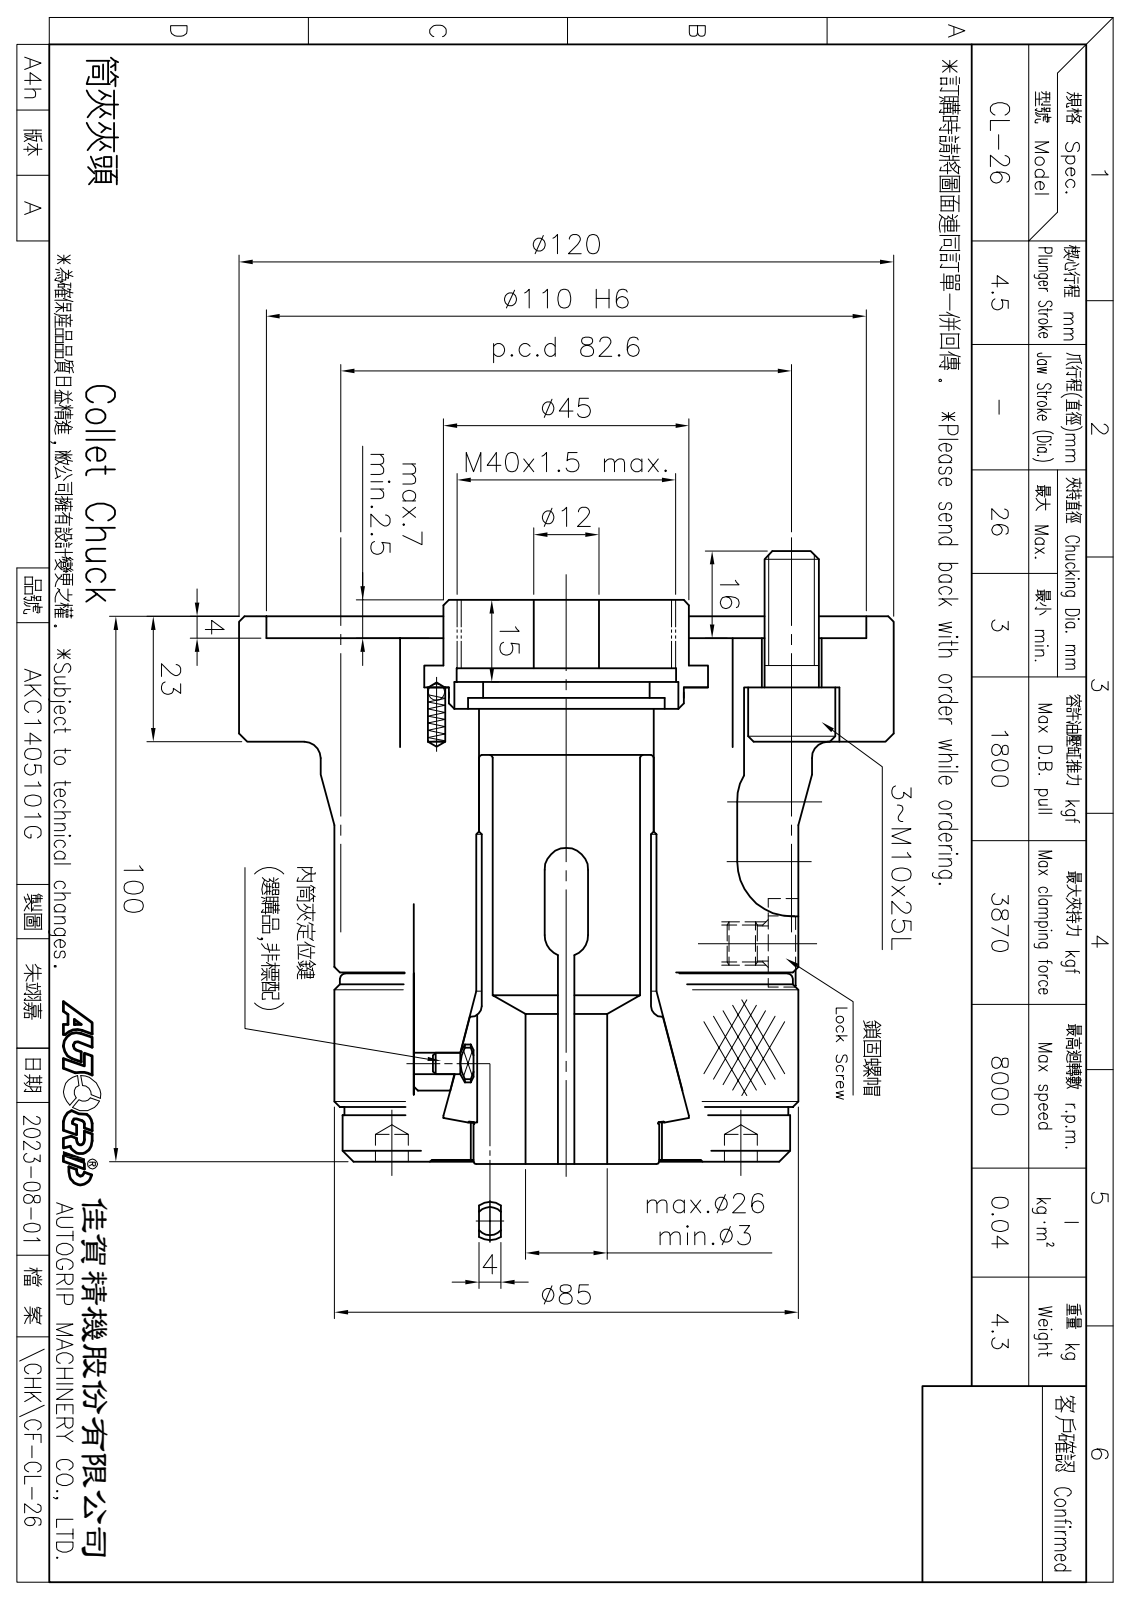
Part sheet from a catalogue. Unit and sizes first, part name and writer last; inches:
Units: inches
Overall size (bounding box): 4.724 × 4.724 × 4.409
Round holes (diameter × count): ⌀0.197 ×3, ⌀0.433 ×3, ⌀0.689 ×3, ⌀0.268 ×1, ⌀1.063 ×1, ⌀1.26 ×1, ⌀1.299 ×1, ⌀1.378 ×1, ⌀1.417 ×1, ⌀1.516 ×1, ⌀1.583 ×1, ⌀1.693 ×1
Round bosses / shafts (diameter × count): ⌀0.63 ×3, ⌀0.394 ×3, ⌀4.724 ×1, ⌀3.543 ×1, ⌀3.346 ×1, ⌀3.268 ×1, ⌀3.228 ×1, ⌀3.205 ×1
Partial cylindrical surfaces — rounded edges, fillets, slot ends (radius × count): R0.335 ×3, R0.394 ×3, R0.148 ×2, R0.315 ×1, R0.325 ×1
Main face-to-face distances: 0.354, 0.335, 3.425, 0.748, 3.031, 2.697, 0.512, 3.78, 3.445, 0.394
Hole centre spacings: 1.626, 2.817, 0.83, 1.24, 2.045, 2.77, 2.48
Volume: 33.63 in³ · Surface area: 207.7 in²
Bodies: 9 solids, 316 faces (97 planar, 114 cylindrical, 105 other)
Part name (STEP PRODUCT): CF-CL-30-04010; CF-CL-26-03000; CF-CL-26; 圓頭內六角螺栓_M10x25 (+4 more)
STEP written by: SolidWorks 2016 (CONFIG_CONTROL_DESIGN)
